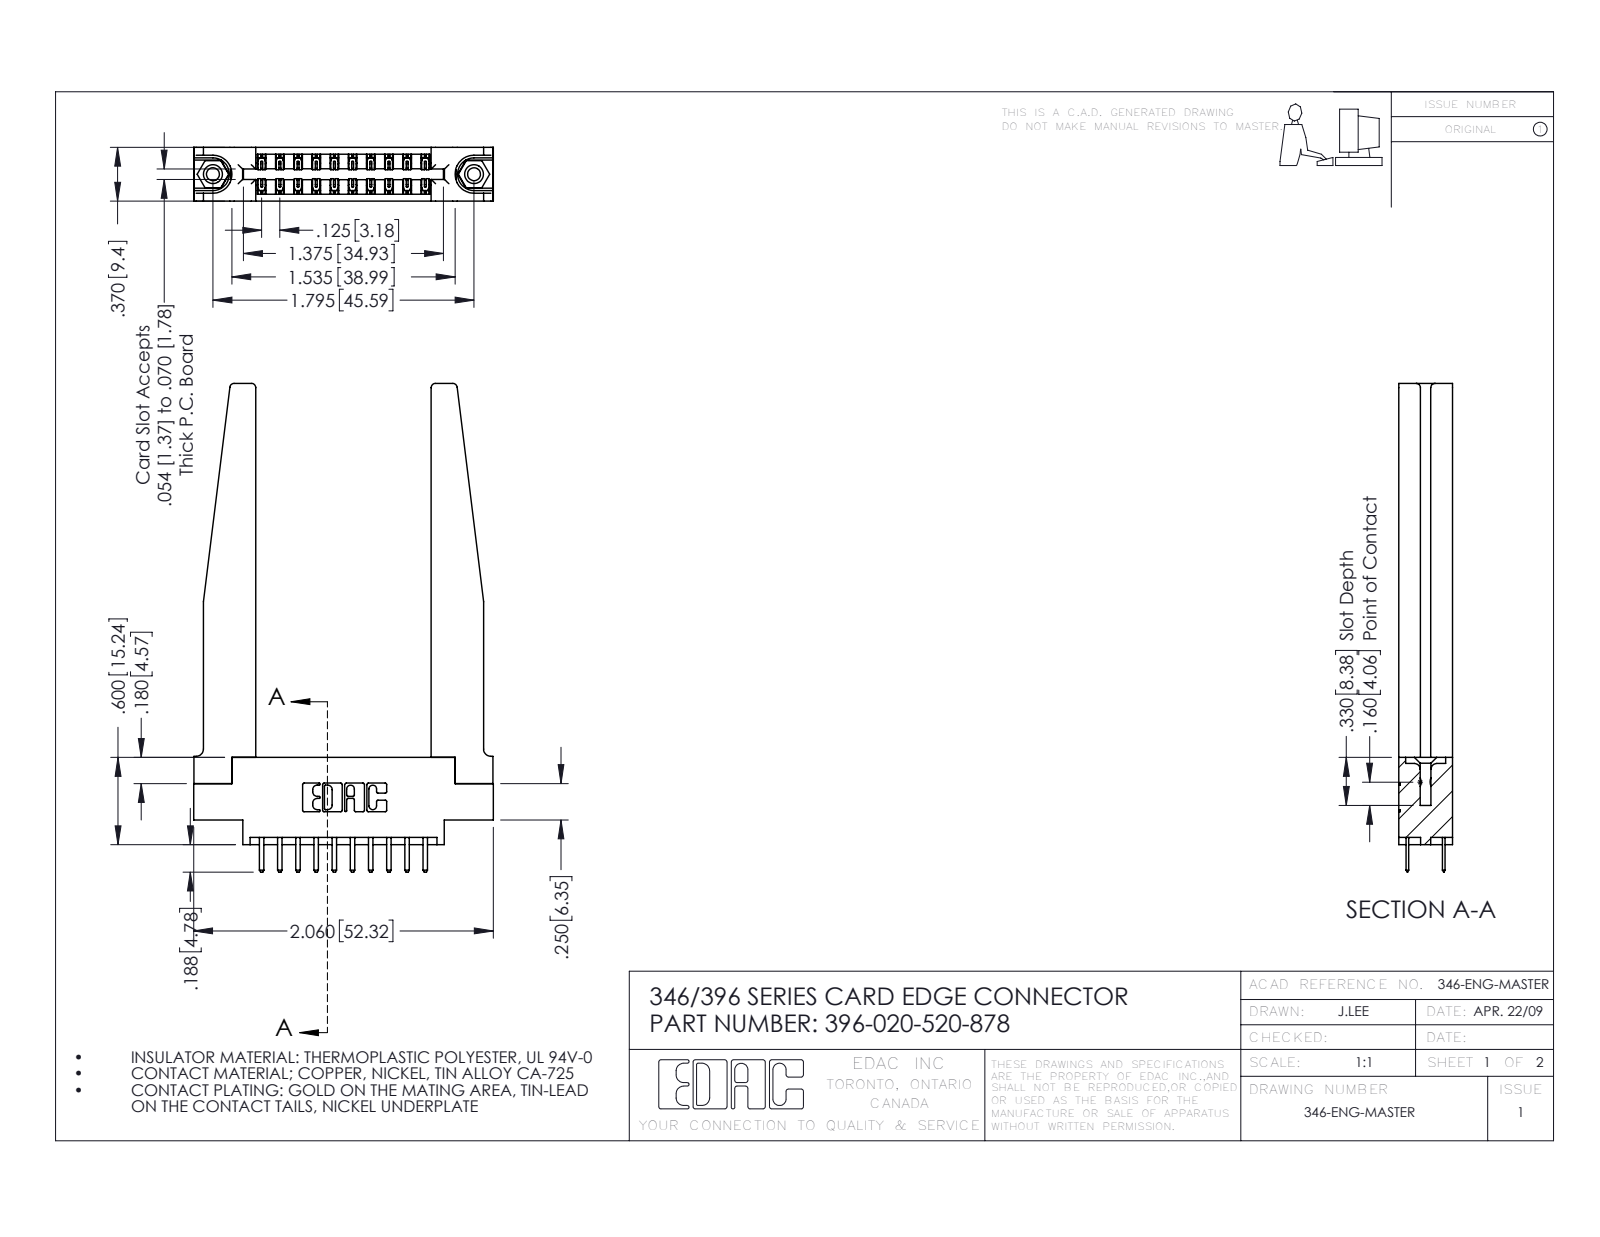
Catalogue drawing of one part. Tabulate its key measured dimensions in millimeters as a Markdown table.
| quantity | value |
| --- | --- |
| part name | 346 Part_0.170 Offset - 0.156 Dia-TH; 345-250-001_345-250-001-102; 345-292-001_345-293-120; 396-020-520-878 (+1 more) |
| STEP written by | SolidWorks 2016 (CONFIG_CONTROL_DESIGN) |
| units | millimeters |
| bodies | 25 solids, 1480 faces (962 planar, 466 cylindrical, 52 other) |
| overall size | 85.3 × 52.3 × 9.4 |
| volume | 11 600 mm³ |
| surface area | 12 640 mm² |
| round holes (diameter × count) | 2.3 × 2, 3.2 × 2, 4 × 2, 1.6 × 1 |
| round bosses / shafts (diameter × count) | 3.9 × 2 |
| partial cylindrical surfaces (radius × count) | 0.2 × 30, 0.3 × 24, 0.3 × 22, 0.8 × 8, 0.2 × 6, 0.8 × 6, 0.7 × 3, 0.4 × 2 |
| main face-to-face distances | 9.4, 3.8, 6.4, 1.8, 3.8, 1.2, 8.2, 2.6, 5.6, 4.4 |
| hole center spacings | 6.2, 40.4, 45.6 |
